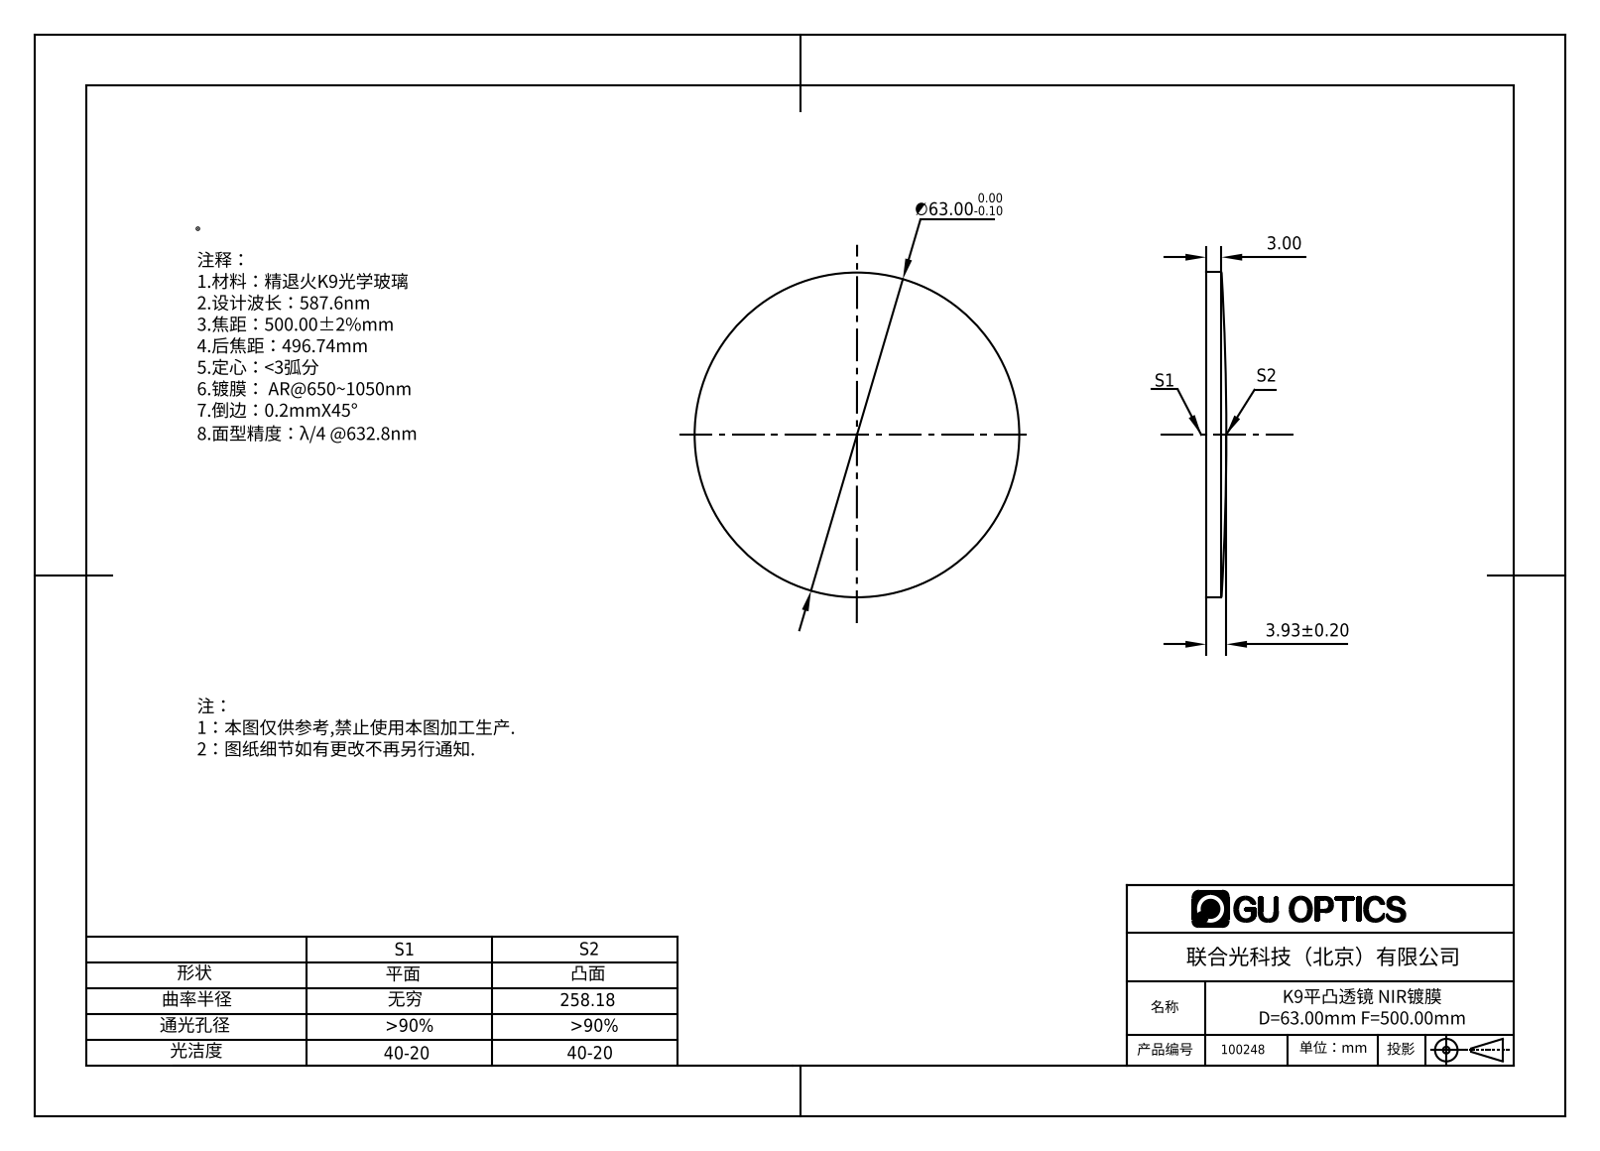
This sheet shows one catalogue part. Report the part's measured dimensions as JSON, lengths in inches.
{"part_name": "100248", "step_written_by": "SolidWorks 2016 (AUTOMOTIVE_DESIGN)", "units": "inches", "bodies": {"solids": 1, "faces": 5, "planar": 1, "cylindrical": 2, "other": 2}, "overall_size": [2.48, 2.48, 0.155], "volume_in3": 0.659, "surface_area_in2": 10.59, "round_bosses_or_shafts": [[2.48, 1]]}
